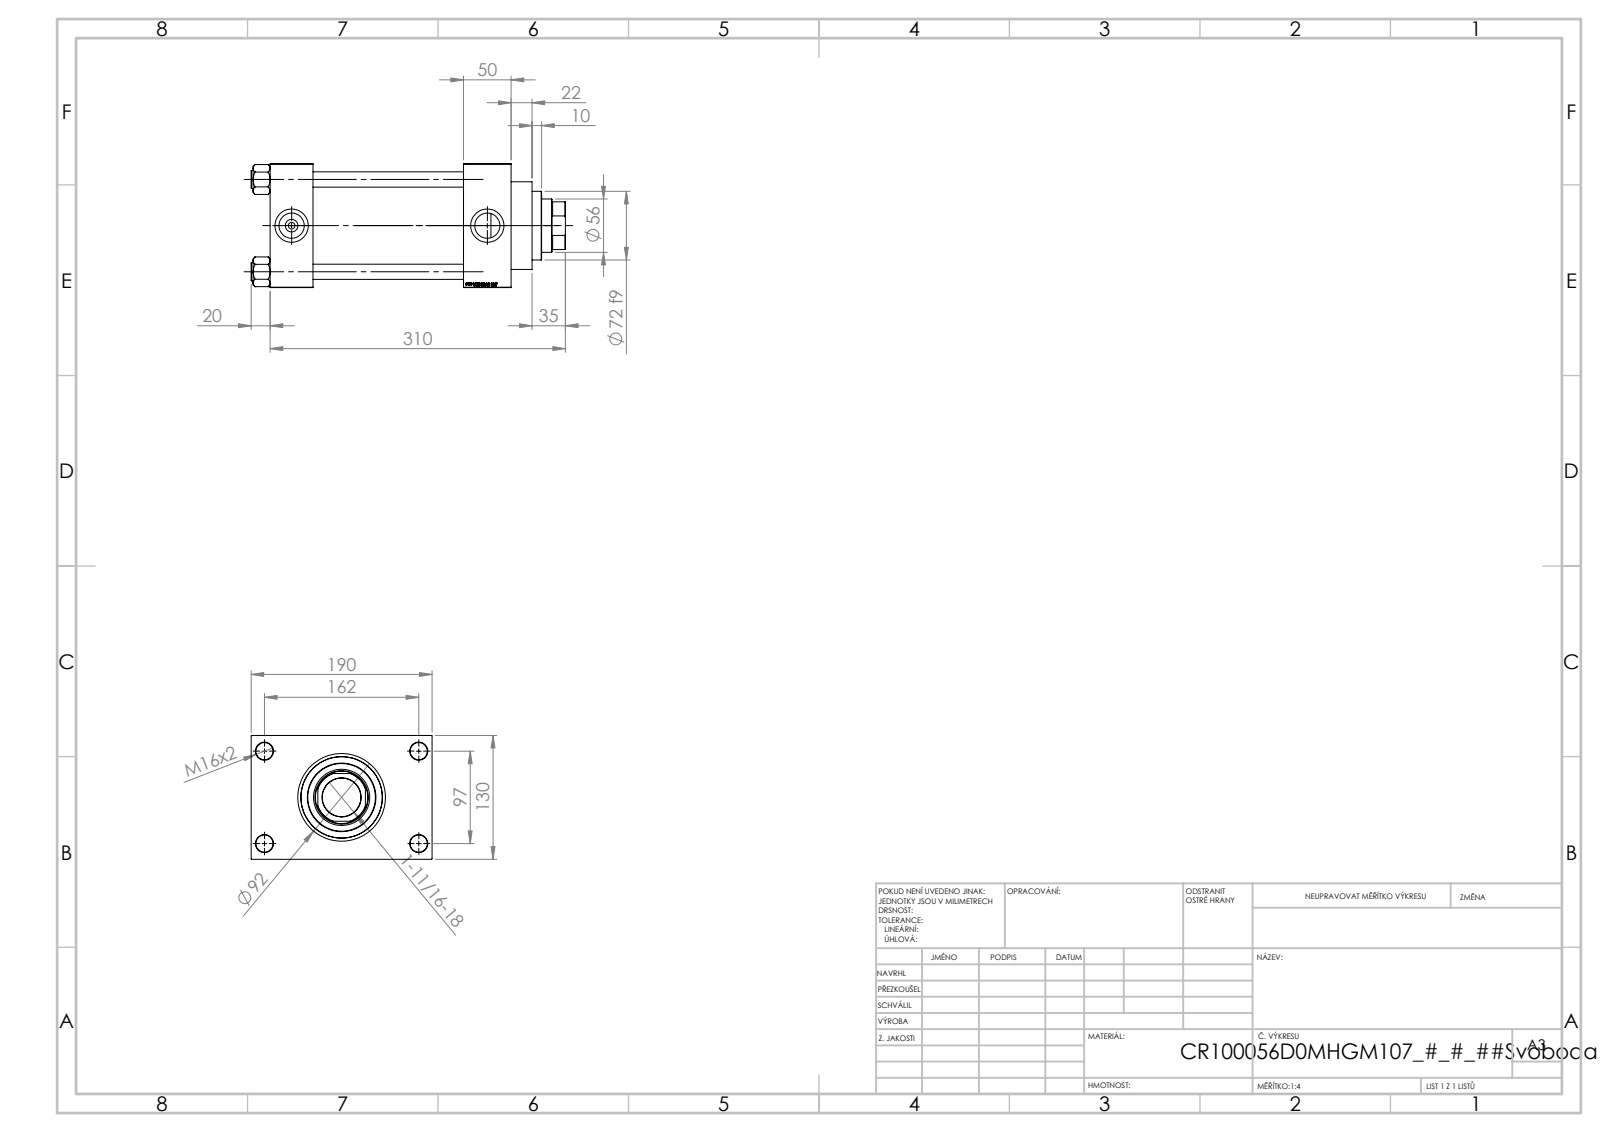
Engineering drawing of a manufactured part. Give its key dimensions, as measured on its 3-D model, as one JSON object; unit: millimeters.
{"part_name": "V215CR_VCP_D; V215CR_D_Body; V215_VC_A; NUT_M5_D (+1 more)", "step_written_by": "SolidWorks 2019 (CONFIG_CONTROL_DESIGN)", "units": "millimeters", "bodies": {"solids": 11, "faces": 1151, "planar": 545, "cylindrical": 88, "other": 518}, "overall_size": [330, 190, 130], "volume_mm3": 2997000, "surface_area_mm2": 451465, "round_holes": [[16, 4], [18, 4], [7, 2], [26.44, 2], [35, 2], [40.5, 1], [56, 1], [59, 1], [76, 1], [85.5, 1], [100, 1]], "round_bosses_or_shafts": [[19, 4], [106, 1], [92, 1], [72, 1]], "partial_cylinders_radius": [[27, 1]], "face_to_face_distances": [130, 50, 45, 158, 203, 253, 208, 30, 160, 107], "hole_center_spacings": [32.55, 68.52, 94.41, 96.9, 102.27, 129.45, 161.73, 97]}
